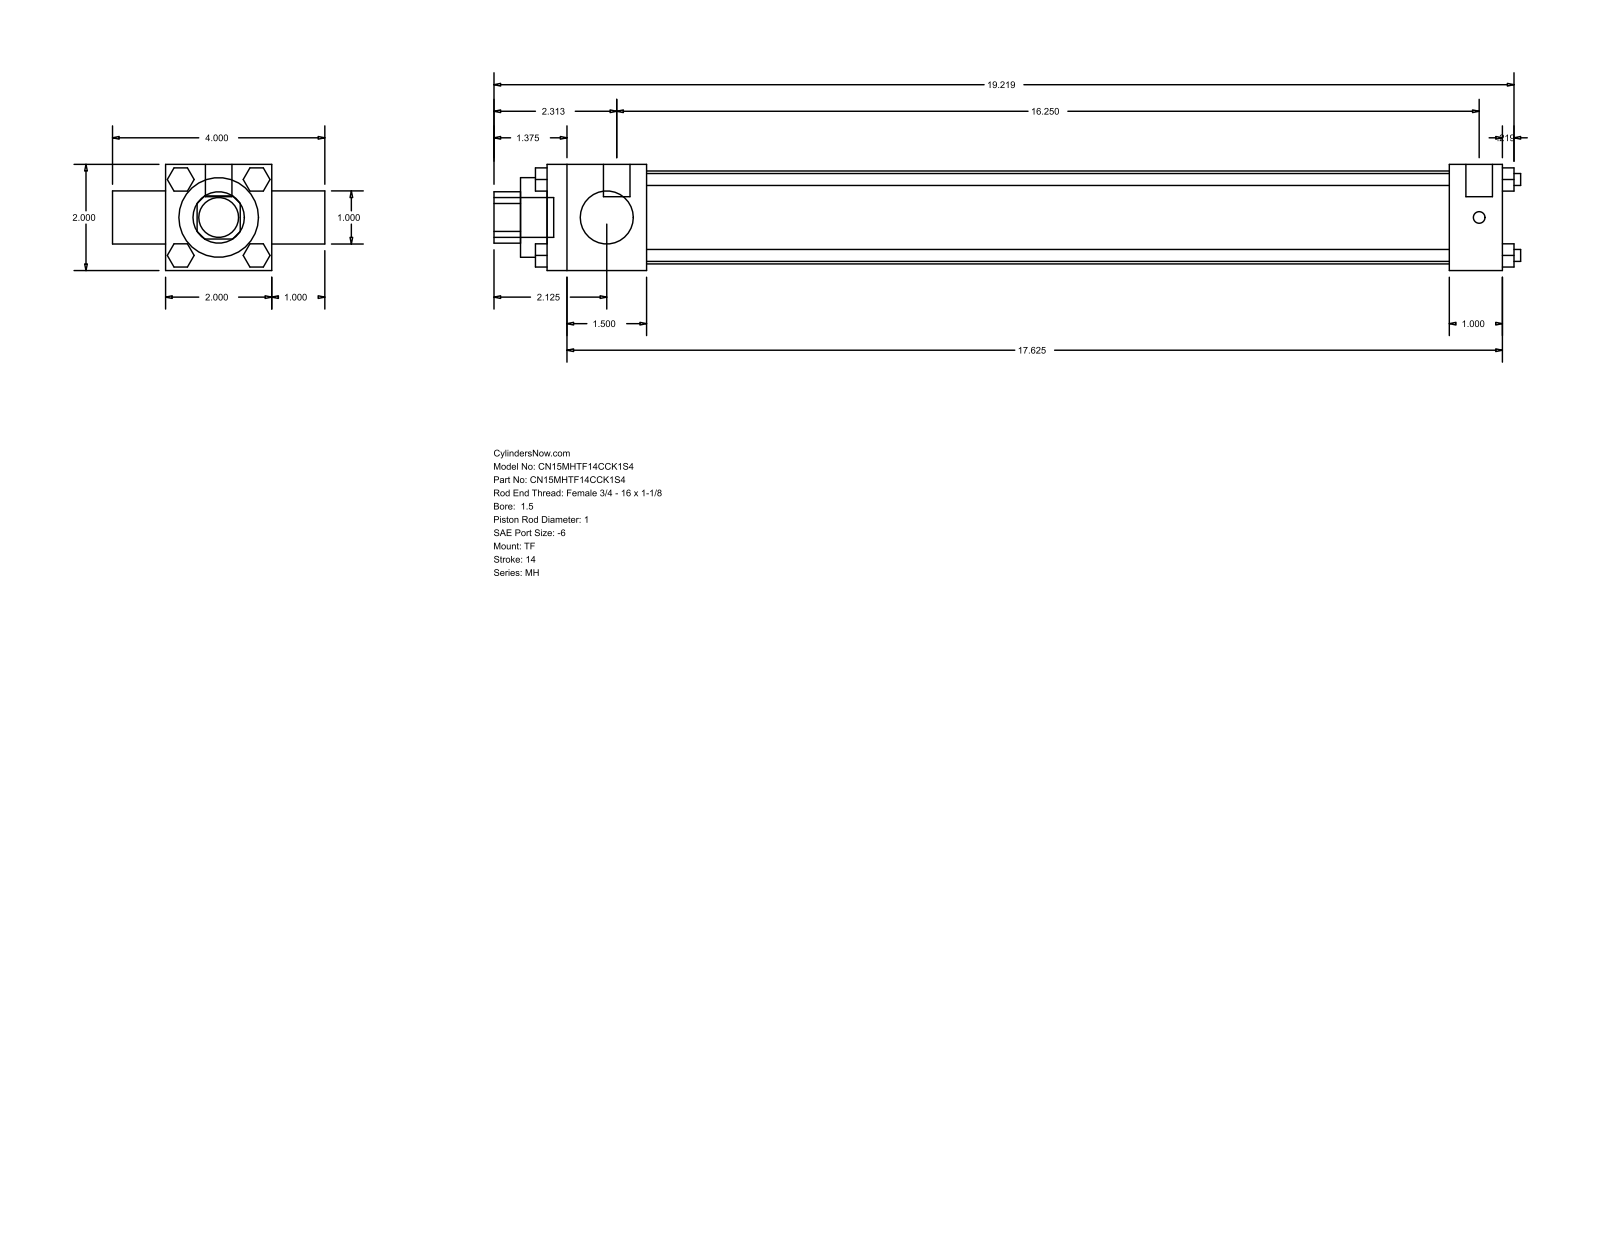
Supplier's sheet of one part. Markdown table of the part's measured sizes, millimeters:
| quantity | value |
| --- | --- |
| part name | MH_TF__0150_1 |
| STEP written by | GSSL Pune (CONFIG_CONTROL_DESIGN) |
| units | millimeters |
| bodies | 0 solids, 120 faces (92 planar, 28 cylindrical, 0 other) |
| overall size | 491.33 × 101.6 × 50.8 |
| round holes (diameter × count) | 25.4 × 2, 38.1 × 1, 44.45 × 1 |
| round bosses / shafts (diameter × count) | 5.71 × 4, 5.56 × 3, 12.7 × 2, 19.05 × 1 |
| partial cylindrical surfaces (radius × count) | 12.29 × 1 |
| main face-to-face distances | 50.8, 25.4, 457.2, 76.2, 47.63, 409.57, 431.8, 384.17, 462.76, 12.7 |
